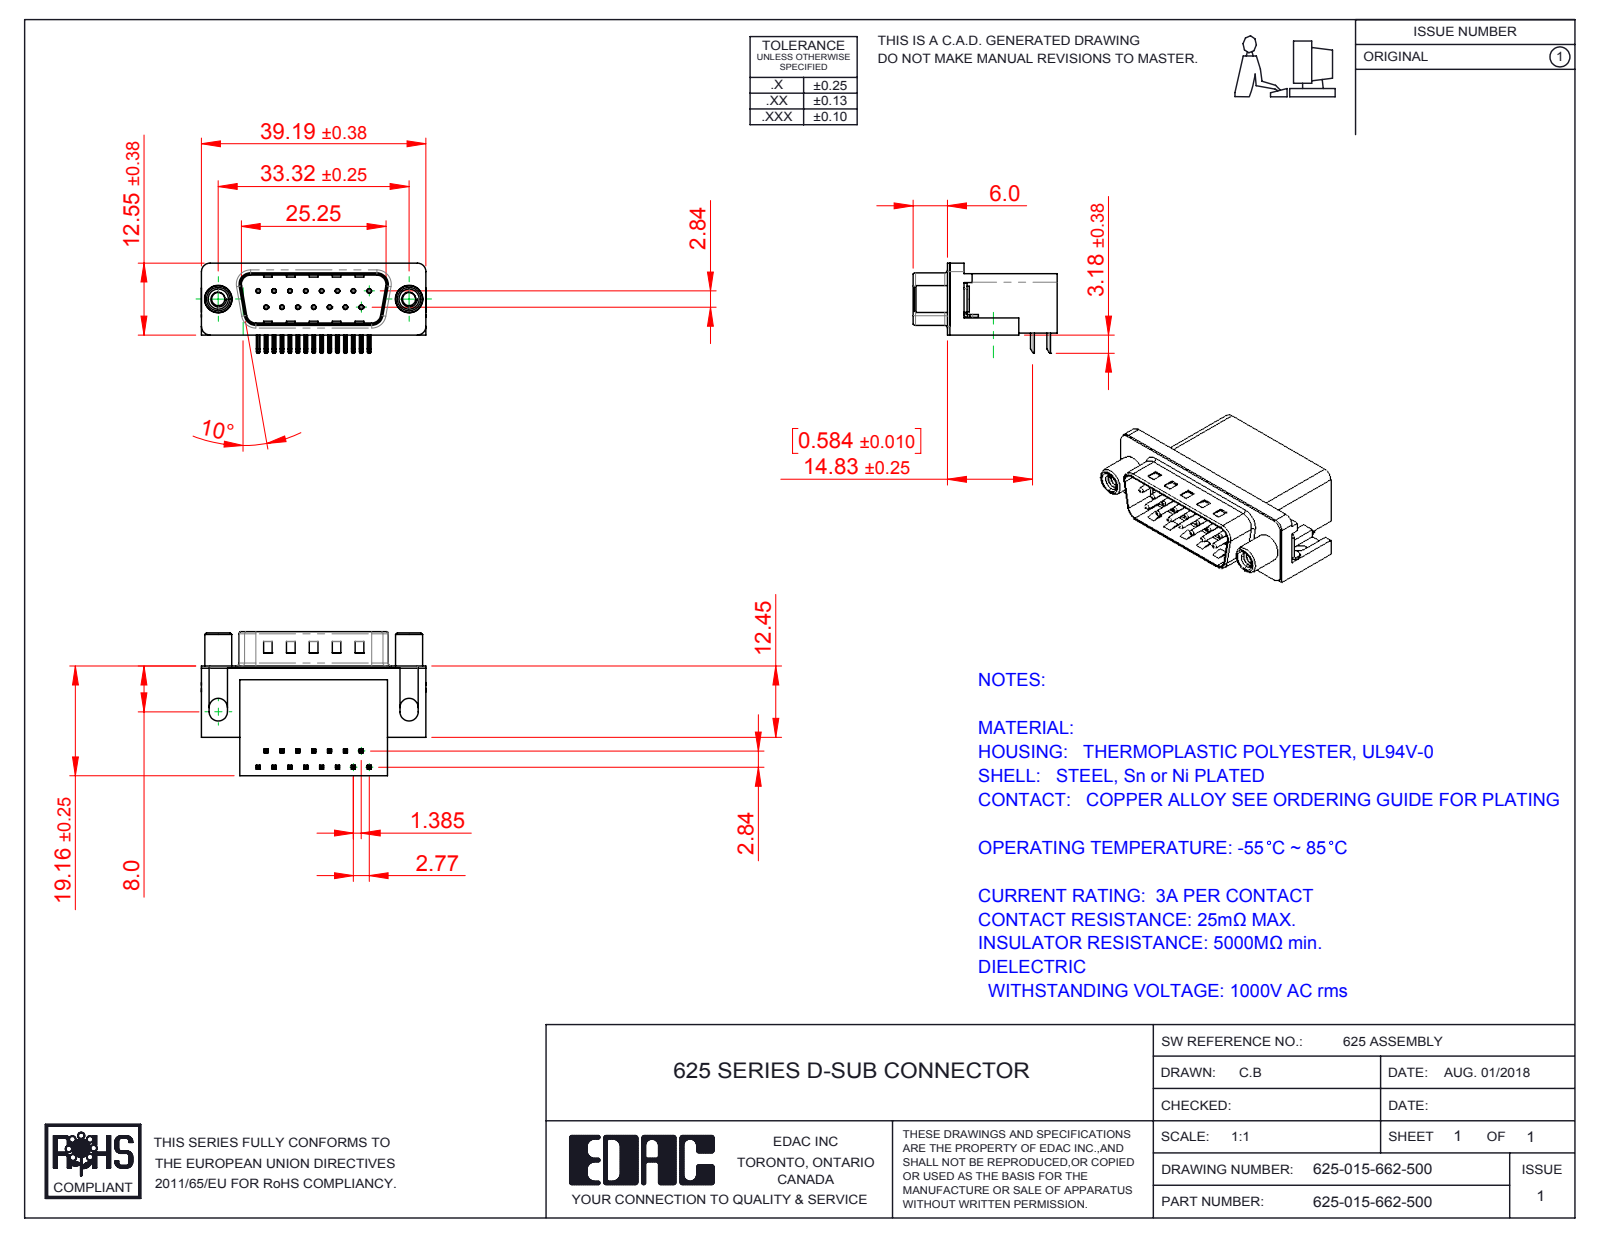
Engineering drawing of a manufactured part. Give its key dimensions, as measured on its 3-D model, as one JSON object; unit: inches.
{"part_name": "625 Contact Bottom; 625 Shell_15 Socket; 625 Round Threaded Standoff; 625-015-662-500 (+3 more)", "step_written_by": "SolidWorks 2016 (CONFIG_CONTROL_DESIGN)", "units": "inches", "bodies": {"solids": 21, "faces": 1471, "planar": 887, "cylindrical": 451, "other": 133}, "overall_size": [1.544, 0.991, 0.619], "volume_in3": 0.385, "surface_area_in2": 10.06, "round_holes": [[0.014, 15], [0.031, 15], [0.091, 2], [0.122, 2], [0.157, 2], [0.189, 2], [0.197, 2]], "round_bosses_or_shafts": [[0.03, 15], [0.193, 2], [0.185, 2], [0.177, 2], [0.152, 2]], "partial_cylinders_radius": [[0.01, 60], [0.005, 30], [0.039, 16], [0.02, 9], [0.063, 8], [0.059, 6], [0.035, 4], [0.079, 4]], "face_to_face_distances": [0.016, 0.407, 0.739, 0.083, 0.412, 0.067, 0.428, 0.754, 0.345, 0.64], "hole_center_spacings": [0.124, 0.109, 0.218, 0.327, 0.436, 0.198, 0.198, 0.294]}
